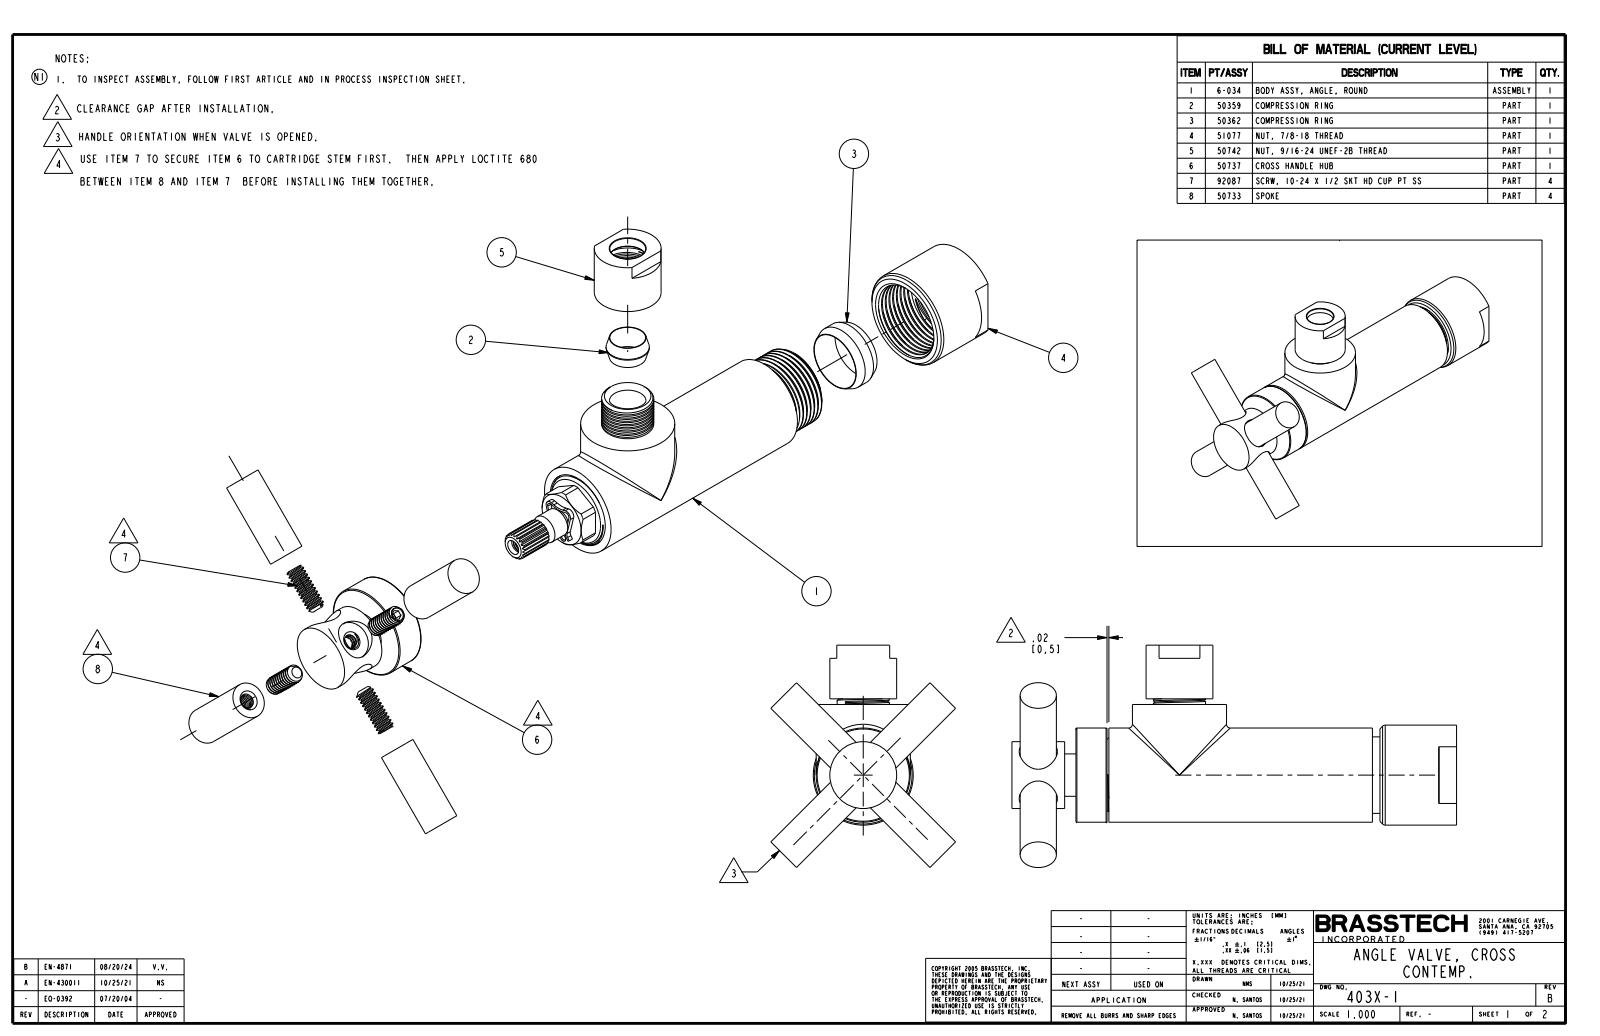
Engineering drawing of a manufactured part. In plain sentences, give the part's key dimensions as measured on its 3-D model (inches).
The part is named "403X-1". Its 3-D file was written by "CREO PARAMETRIC BY PTC INC, 2018500 (CONFIG_CONTROL_DESIGN)". It is 6 solids with 1074 faces: 244 planar, 513 cylindrical and 317 other. Overall it measures 4.724 by 2.361 by 1.963 inches. Its volume is 2.006 cubic inches and its surface area 80.75 square inches. Round holes: 2 of diameter 0.145, 2 of diameter 0.15, 2 of diameter 0.19, 2 of diameter 0.385, 2 of diameter 0.406, 1 of diameter 0.145, 1 of diameter 0.275, 1 of diameter 0.3, 1 of diameter 0.32, 1 of diameter 0.328, 1 of diameter 0.38, 1 of diameter 0.382. Round bosses or shafts: 2 of diameter 1, 2 of diameter 0.385, 1 of diameter 0.893, 1 of diameter 0.885, 1 of diameter 0.819, 1 of diameter 0.805, 1 of diameter 0.776, 1 of diameter 0.776. Partial cylindrical surfaces (rounded edges, fillets, slot ends): 2 of radius 0.005, 2 of radius 0.04, 2 of radius 0.057, 2 of radius 0.063, 2 of radius 0.08, 1 of radius 0.134, 1 of radius 0.277, 1 of radius 0.3. The main face-to-face distances are 4.044, 2.294, 1.75, 0.814, 1.48, 3.23, 4.724, 3.91, 2.43, 0.68. The hole center spacings are 0.043.
